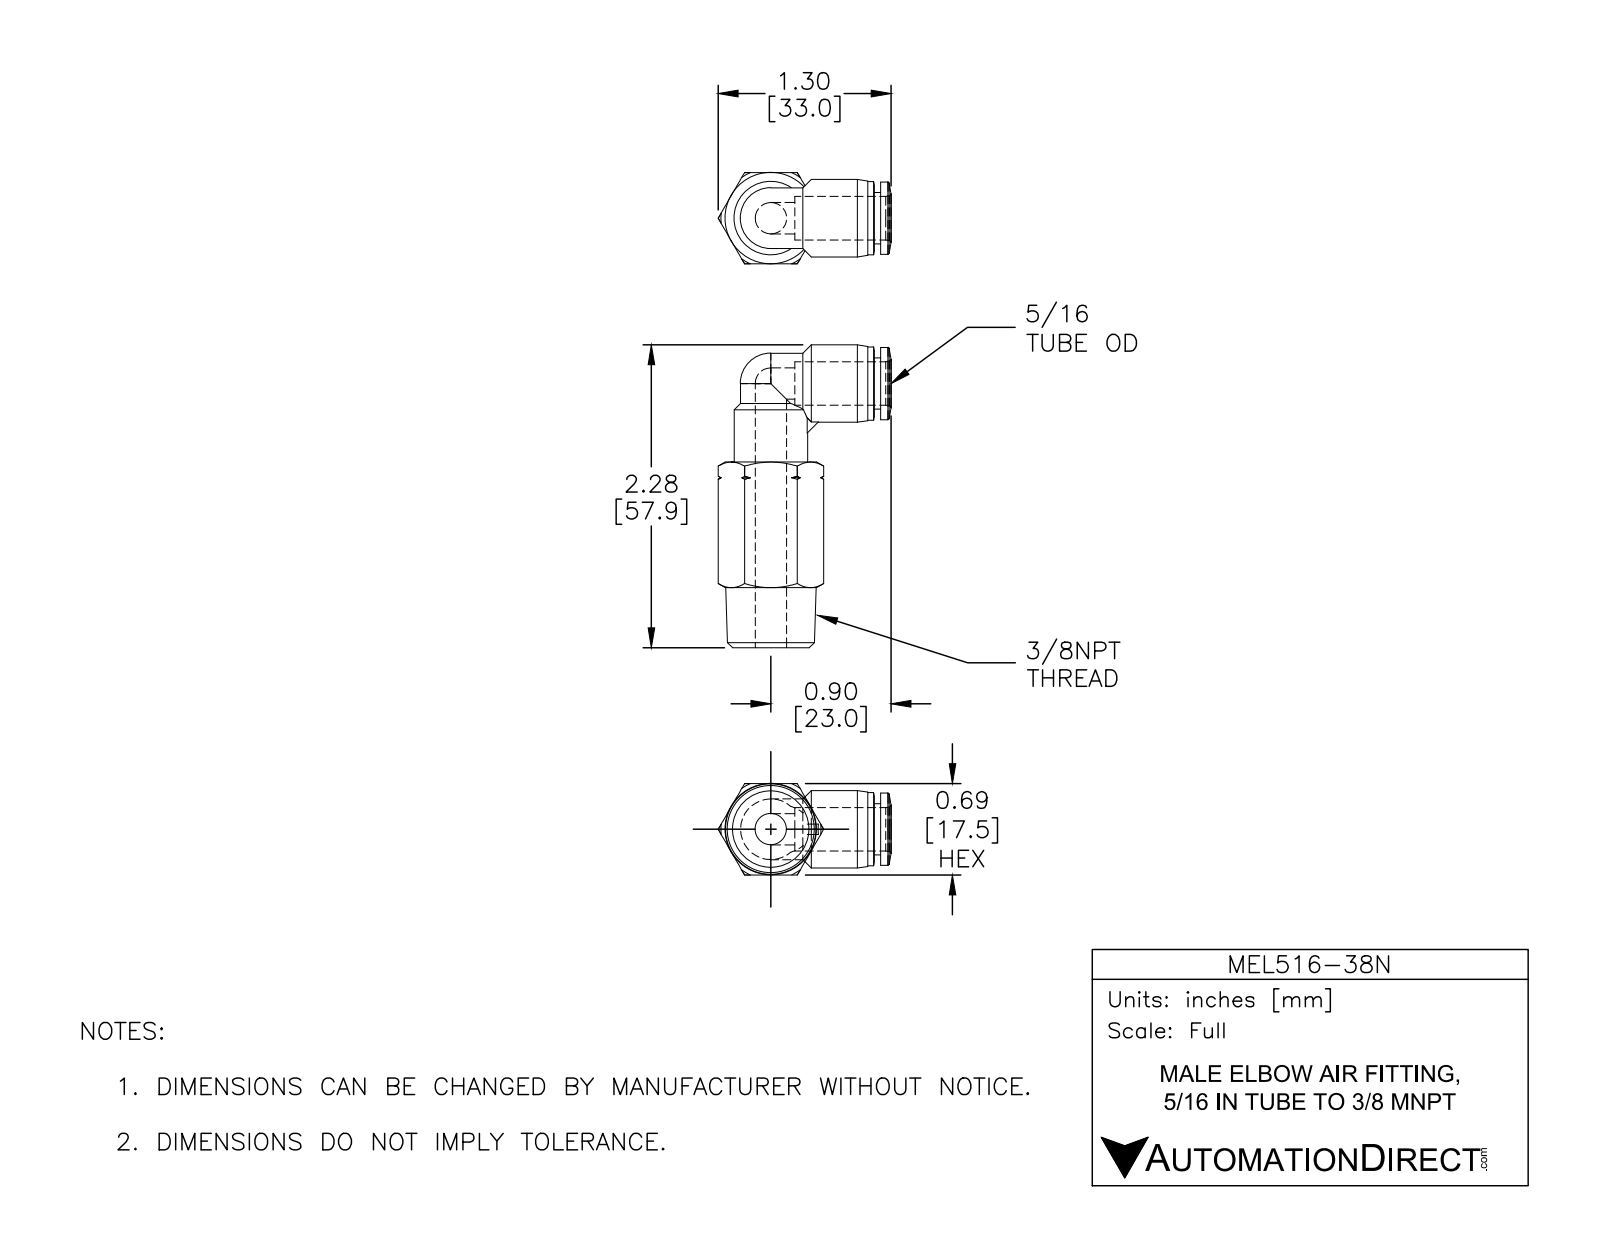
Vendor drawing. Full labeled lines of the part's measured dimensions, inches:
Part name (STEP PRODUCT): MEL516-38N
STEP written by: SolidWorks 2015 (CONFIG_CONTROL_DESIGN)
Units: inches
Bodies: 1 solid, 89 faces (16 planar, 21 cylindrical, 52 other)
Overall size (bounding box): 2.28 × 1.3 × 0.687
Volume: 0.711 in³ · Surface area: 8.819 in²
Round holes (diameter × count): ⌀0.236 ×2, ⌀0.327 ×1
Round bosses / shafts (diameter × count): ⌀0.551 ×2, ⌀0.583 ×1, ⌀0.543 ×1, ⌀0.457 ×1, ⌀0.386 ×1
Partial cylindrical surfaces — rounded edges, fillets, slot ends (radius × count): R0.228 ×1
Main face-to-face distances: 0.687, 1.398, 0.047, 0.598, 0.646, 0.304, 0.383, 0.549, 0.049, 0.096
